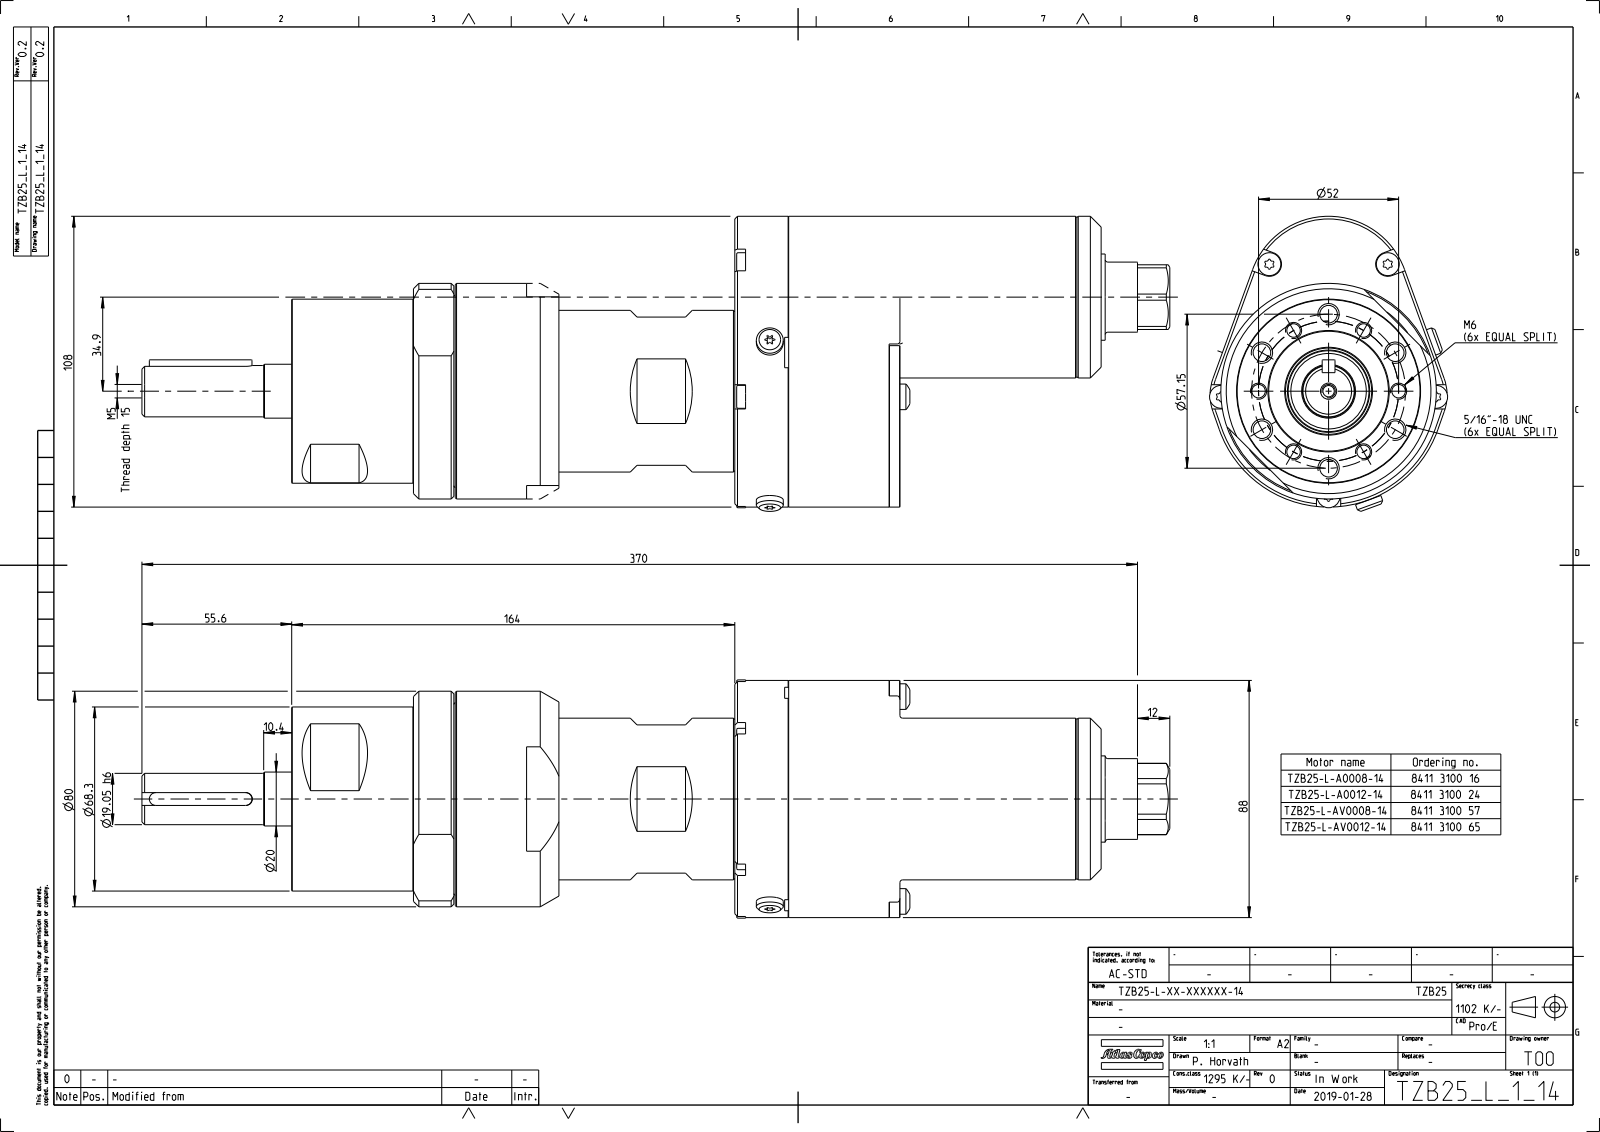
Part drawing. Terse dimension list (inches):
name: 8411310016_SW0002
written by: CREO PARAMETRIC BY PTC INC, 2022414 (AP242_MANAGED_MODEL_BASED_3D_ENGINEERING_MIM_LF)
unit: in
bodies: 1 solid, 762 faces (274 planar, 249 cylindrical, 239 other)
size: 15.024 × 4.311 × 3.48
volume: 76.96 in³; area: 159.9 in²
holes: 6× ⌀0.197, 6× ⌀0.257, 1× ⌀0.165, 1× ⌀0.61, 1× ⌀1.75
bosses: 5× ⌀0.335, 2× ⌀2.362, 2× ⌀0.394, 2× ⌀0.374, 1× ⌀3.15, 1× ⌀2.689, 1× ⌀2.638, 1× ⌀1.26
rounds: 30× R0.015, 30× R0.027, 24× R0.005, 16× R0.008, 12× R0.012, 12× R0.019, 12× R0.033, 9× R0.039
face distances: 2.413, 8.89, 6.476, 6.5, 4.087, 2.39, 2.941, 5.354, 9.441, 11.831
hole spacings: 1.024, 0.565, 1.521, 2.076, 1.125, 1.125, 0.565, 1.521
